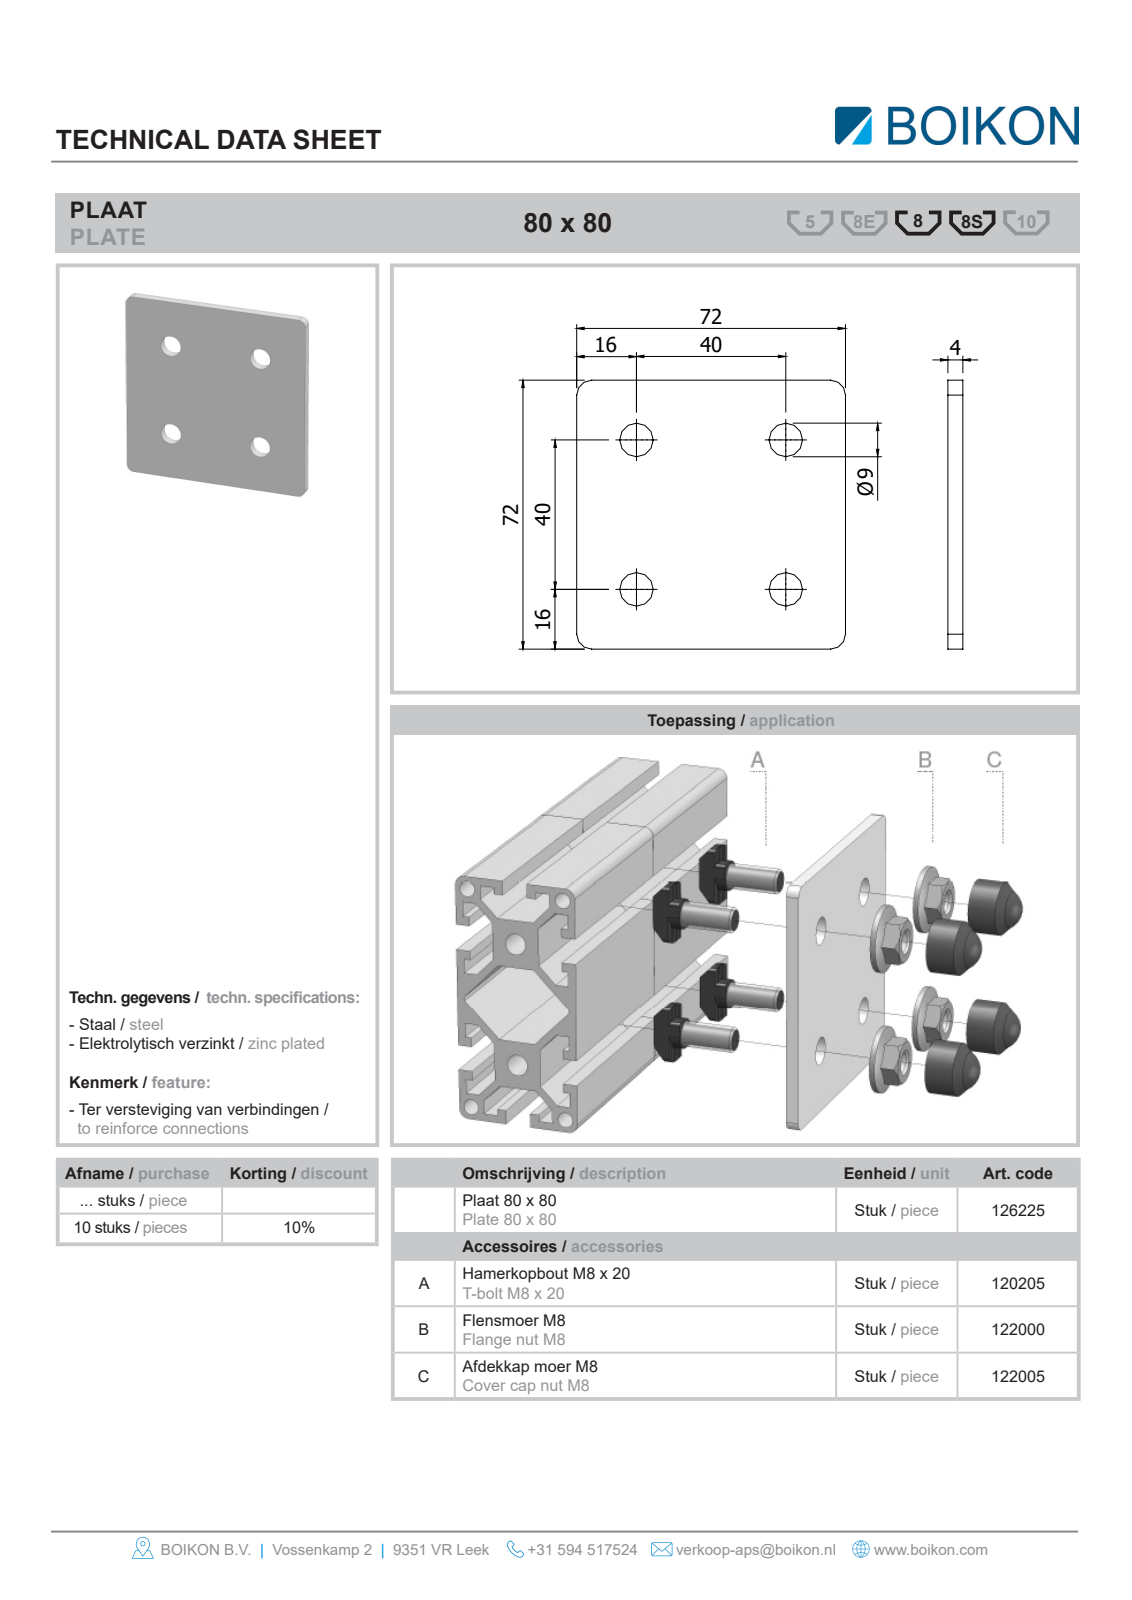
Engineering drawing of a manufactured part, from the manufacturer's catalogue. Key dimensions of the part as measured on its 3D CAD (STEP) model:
Part name (STEP PRODUCT): Root; 126225 Plaat 80 x 80BOIKON; 122000Flensmoer M8BOIKON; 122005Afdekkap voor moer M8BOIKON (+1 more)
STEP written by: HiCAD 2013 1802.4 Build 509 (AUTOMOTIVE_DESIGN)
Units: millimetres
Bodies: 13 solids, 366 faces (250 planar, 64 cylindrical, 52 other)
Overall size (bounding box): 80 × 80 × 31.8
Volume: 44 070 mm³ · Surface area: 27 710 mm²
Round holes (diameter × count): ⌀8 ×4, ⌀9 ×4
Round bosses / shafts (diameter × count): ⌀21 ×4, ⌀16.8 ×4, ⌀6.47 ×4
Partial cylindrical surfaces — rounded edges, fillets, slot ends (radius × count): R1 ×20, R5 ×8, R1.16 ×4, R3 ×4, R9.5 ×4
Main face-to-face distances: 4, 7, 13, 40, 80, 11, 34.64, 20, 8, 5.5
Hole centre spacings: 40, 56.57
